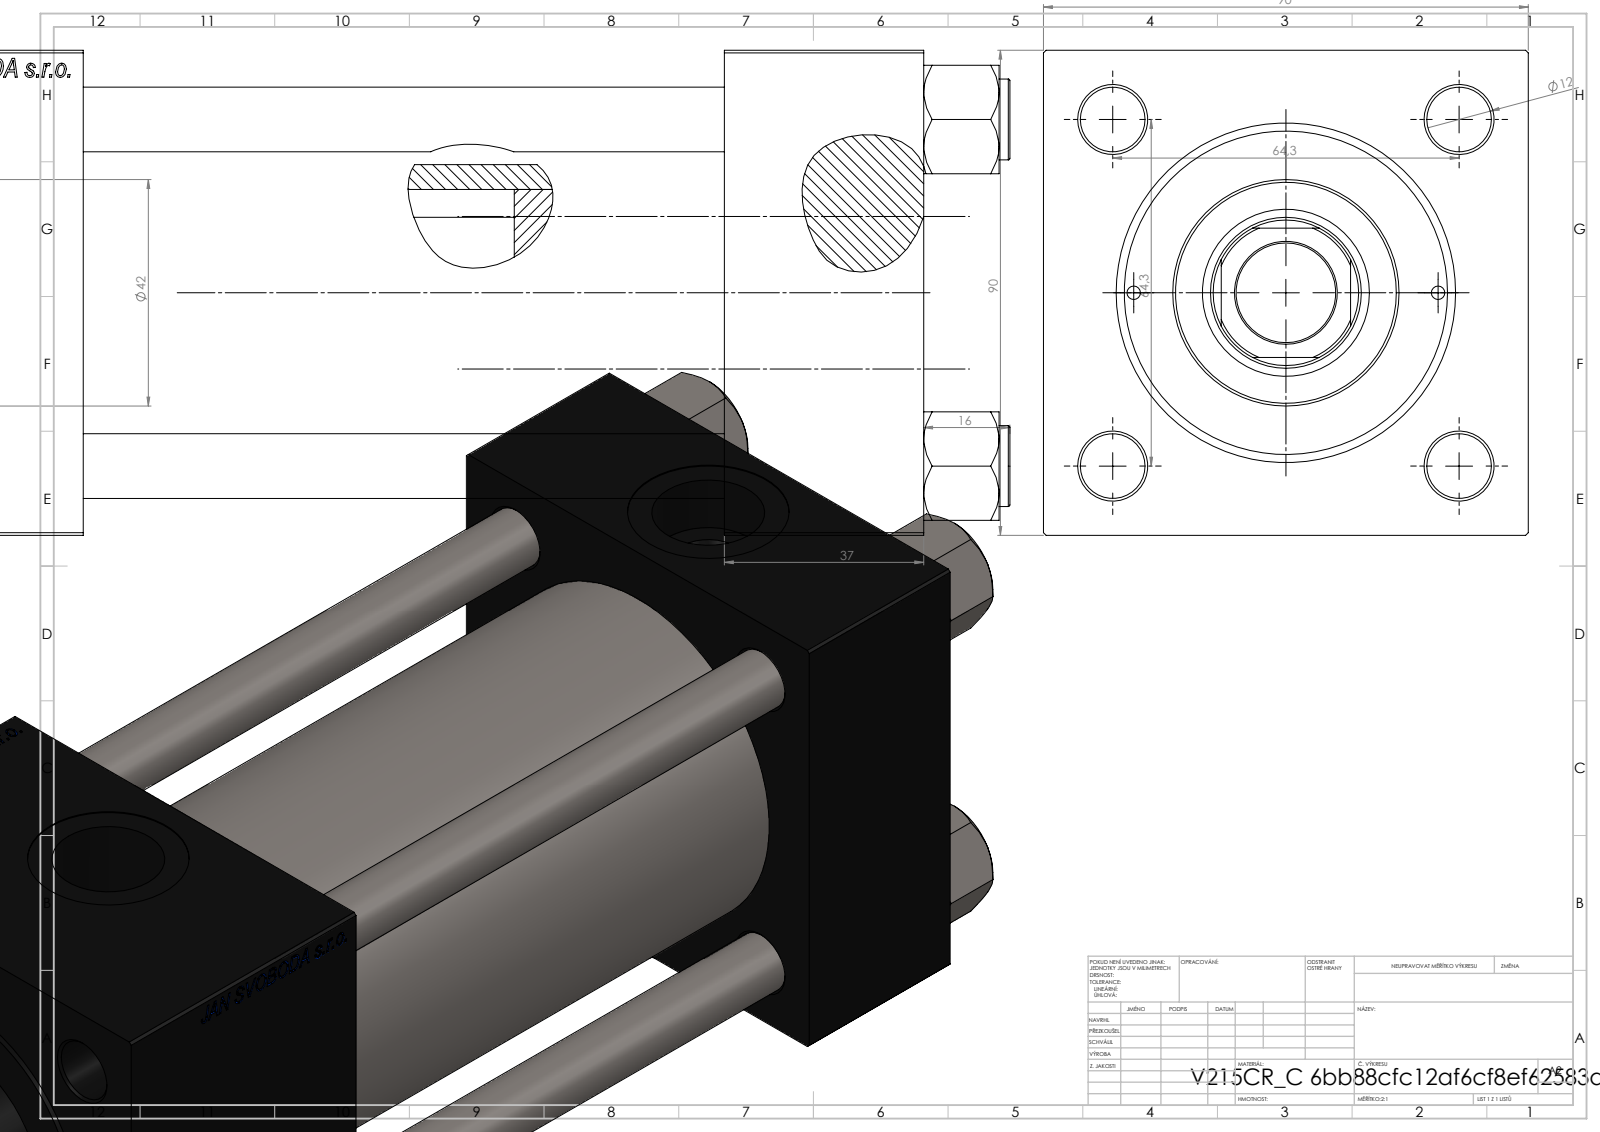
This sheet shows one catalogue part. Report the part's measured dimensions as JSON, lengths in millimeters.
{"part_name": "NUT_M5_C; V215CR_C_TYCINKA; V215_VC_A; V215CR_C_Body (+1 more)", "step_written_by": "SolidWorks 2019 (CONFIG_CONTROL_DESIGN)", "units": "millimeters", "bodies": {"solids": 11, "faces": 1155, "planar": 528, "cylindrical": 91, "other": 536}, "overall_size": [263, 90, 90], "volume_mm3": 1048000, "surface_area_mm2": 218419, "round_holes": [[12, 4], [2.5, 2], [7, 2], [20.96, 2], [30, 2], [18.5, 1], [28, 1], [31, 1], [50, 1], [60, 1], [63, 1]], "round_bosses_or_shafts": [[15, 4], [69, 1], [42, 1]], "partial_cylinders_radius": [[13.5, 1]], "face_to_face_distances": [90, 37, 215, 178, 156, 119, 59, 186.3, 149.3, 30.3], "hole_center_spacings": [32.39, 45.47, 64.3, 68.42, 28.25, 90.93, 56.5, 157.5]}
